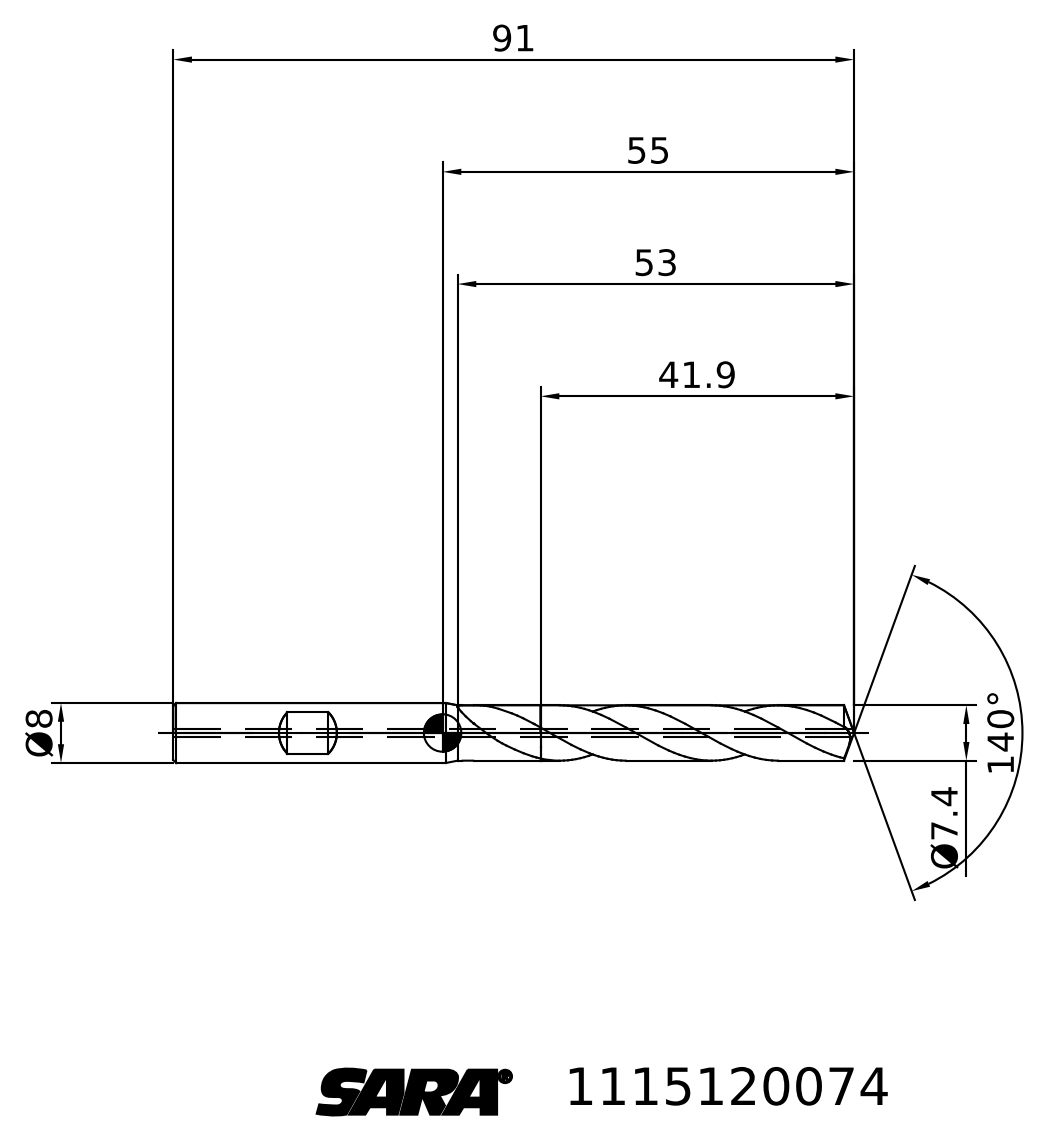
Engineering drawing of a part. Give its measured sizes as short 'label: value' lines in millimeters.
written by: TDM (AUTOMOTIVE_DESIGN)
unit: mm
bodies: 2 solids, 31 faces (6 planar, 0 cylindrical, 25 other)
size: 91 × 9.04 × 8
volume: 3 378 mm³; area: 2 402 mm²
face distances: 49.1
